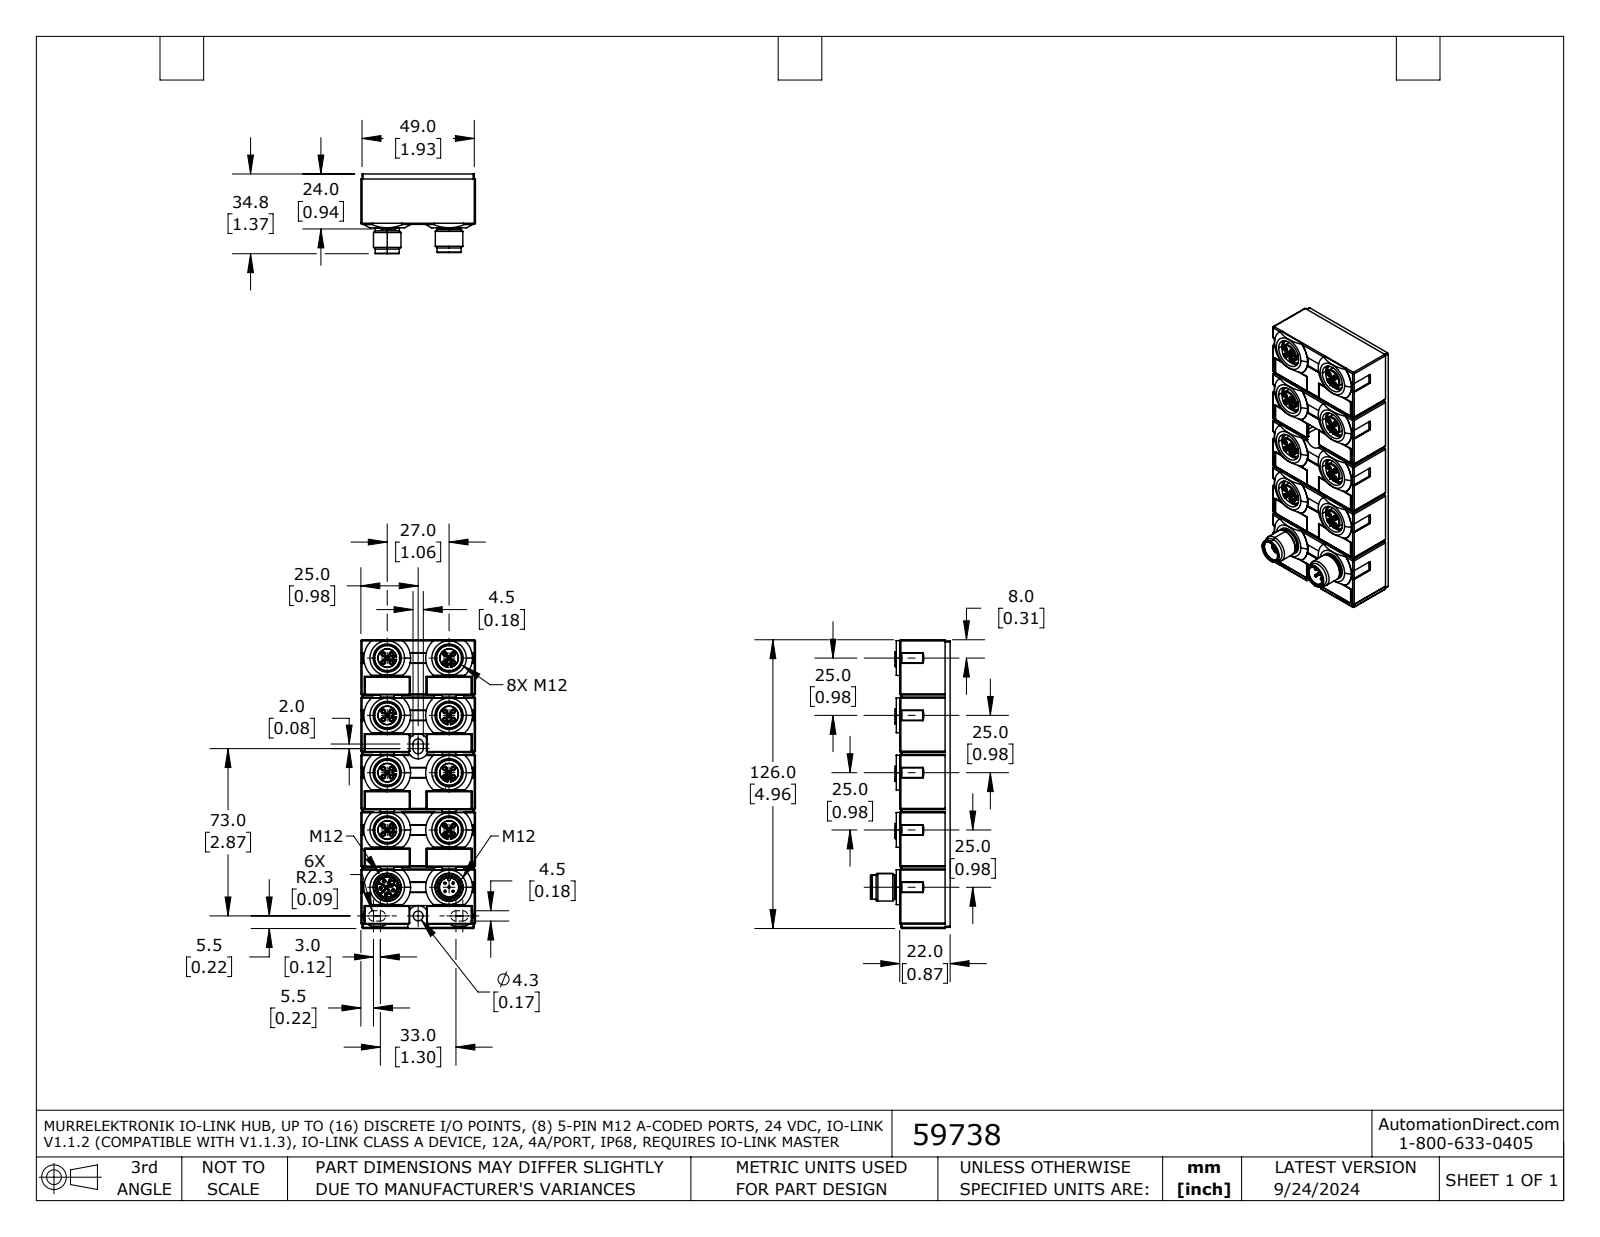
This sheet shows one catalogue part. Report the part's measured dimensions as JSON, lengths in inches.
{"part_name": "59738", "step_written_by": "SolidWorks 2021 (AUTOMOTIVE_DESIGN)", "units": "inches", "bodies": {"solids": 1, "faces": 1461, "planar": 514, "cylindrical": 625, "other": 322}, "overall_size": [4.961, 1.969, 1.37], "volume_in3": 8.233, "surface_area_in2": 47.02, "round_holes": [[0.047, 40], [0.484, 8], [0.43, 7], [0.065, 1], [0.169, 1], [0.327, 1], [0.35, 1], [0.43, 1]], "round_bosses_or_shafts": [[0.079, 40], [0.323, 8], [0.039, 5], [0.059, 4], [0.472, 2], [0.413, 2]], "partial_cylinders_radius": [[0.02, 81], [0.01, 48], [0.394, 15], [0.004, 13], [0.402, 10], [0.024, 8], [0.045, 8], [0.401, 8]], "face_to_face_distances": [1.969, 0.02, 0.864, 0.866, 0.059, 0.061, 0.925, 4.961, 1.949, 0.984], "hole_center_spacings": [0.098, 0.139, 0.984, 1.449, 1.056, 0.917, 0.994, 1.063]}
